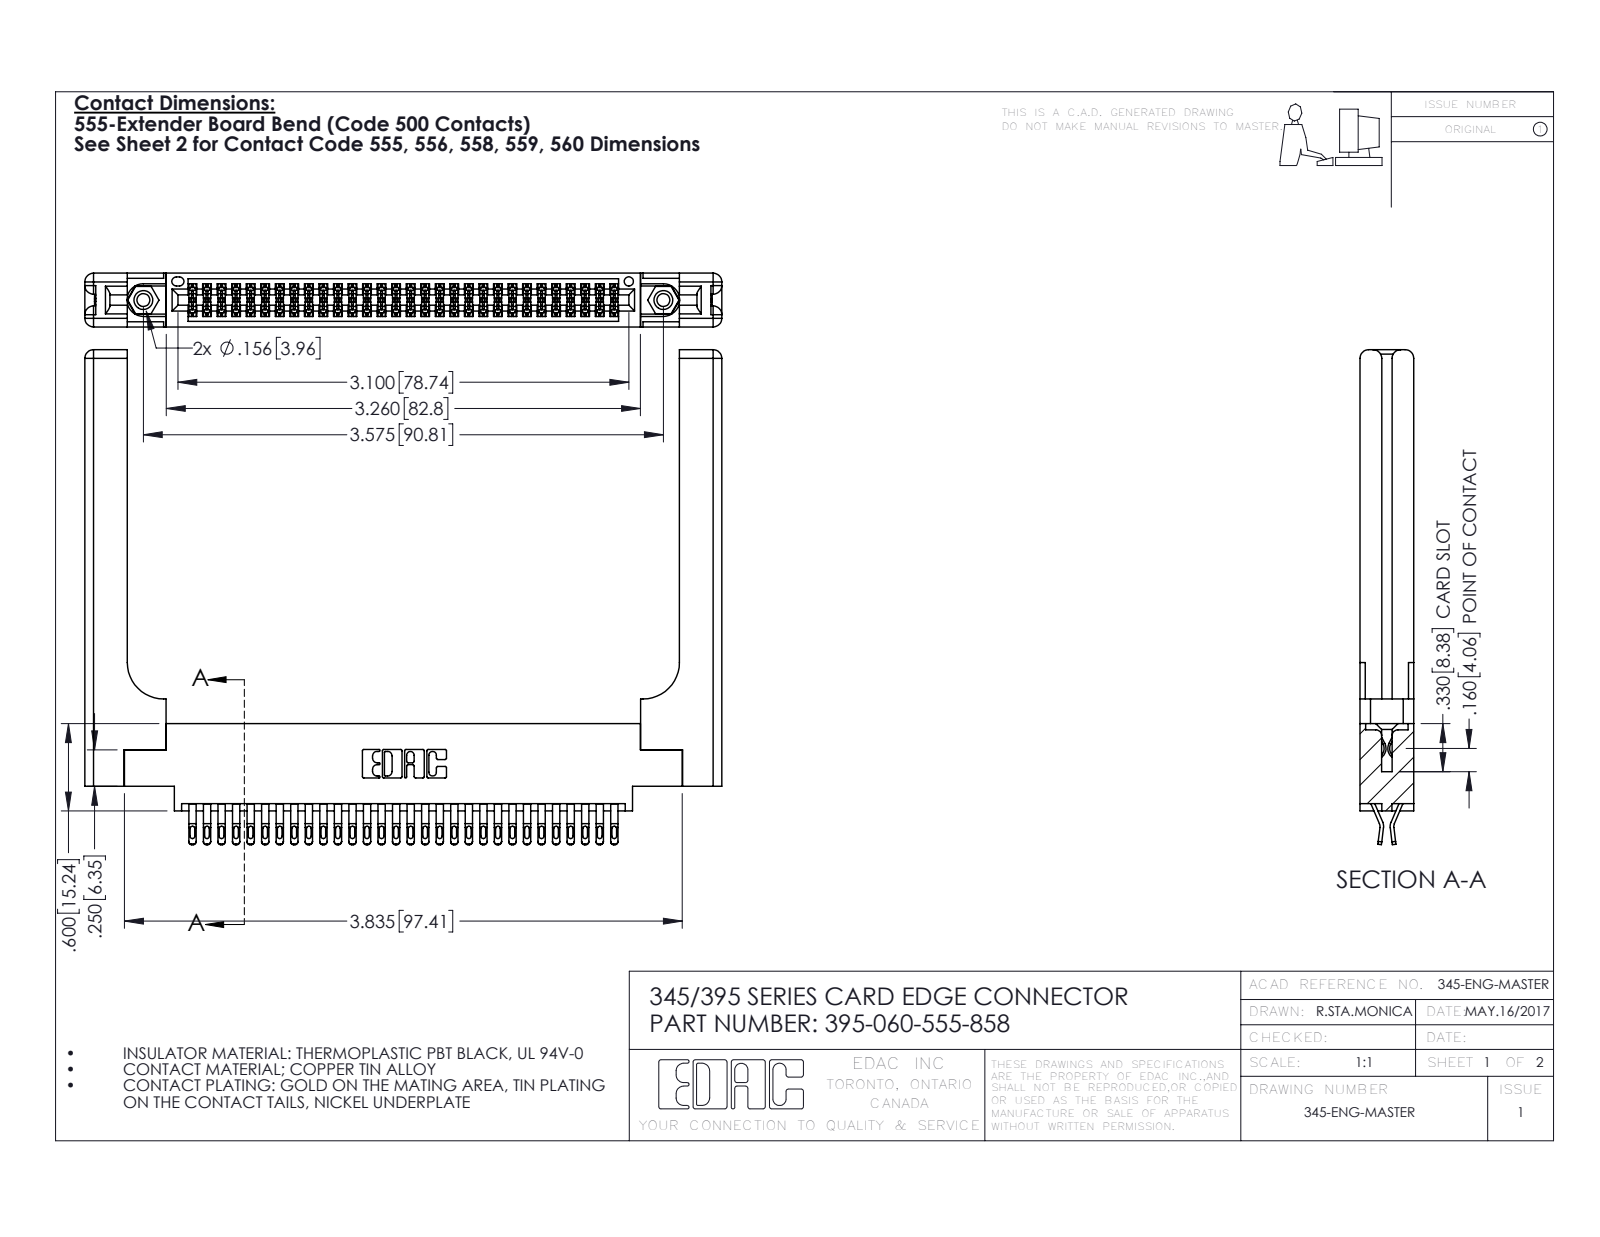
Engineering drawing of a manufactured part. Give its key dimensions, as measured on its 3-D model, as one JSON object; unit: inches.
{"part_name": "345-250-001_345-250-001-102; 345-292-001_555 Tail; 345 Part_0.170 Offset - 0.156 Dia-TH; 345-220-058_345-220-058 (+1 more)", "step_written_by": "SolidWorks 2016 (CONFIG_CONTROL_DESIGN)", "units": "inches", "bodies": {"solids": 65, "faces": 3746, "planar": 2092, "cylindrical": 1594, "other": 60}, "overall_size": [4.379, 3.402, 0.37], "volume_in3": 1.173, "surface_area_in2": 33.28, "round_holes": [[0.089, 2], [0.125, 2], [0.156, 2], [0.064, 1]], "round_bosses_or_shafts": [[0.155, 2]], "partial_cylinders_radius": [[0.016, 150], [0.02, 120], [0.006, 90], [0.01, 22], [0.06, 16], [0.007, 6], [0.031, 6], [0.026, 3]], "face_to_face_distances": [0.37, 0.072, 0.298, 0.025, 0.225, 0.098, 0.272, 0.2, 0.148, 0.15], "hole_center_spacings": [0.27, 3.34, 3.575]}
